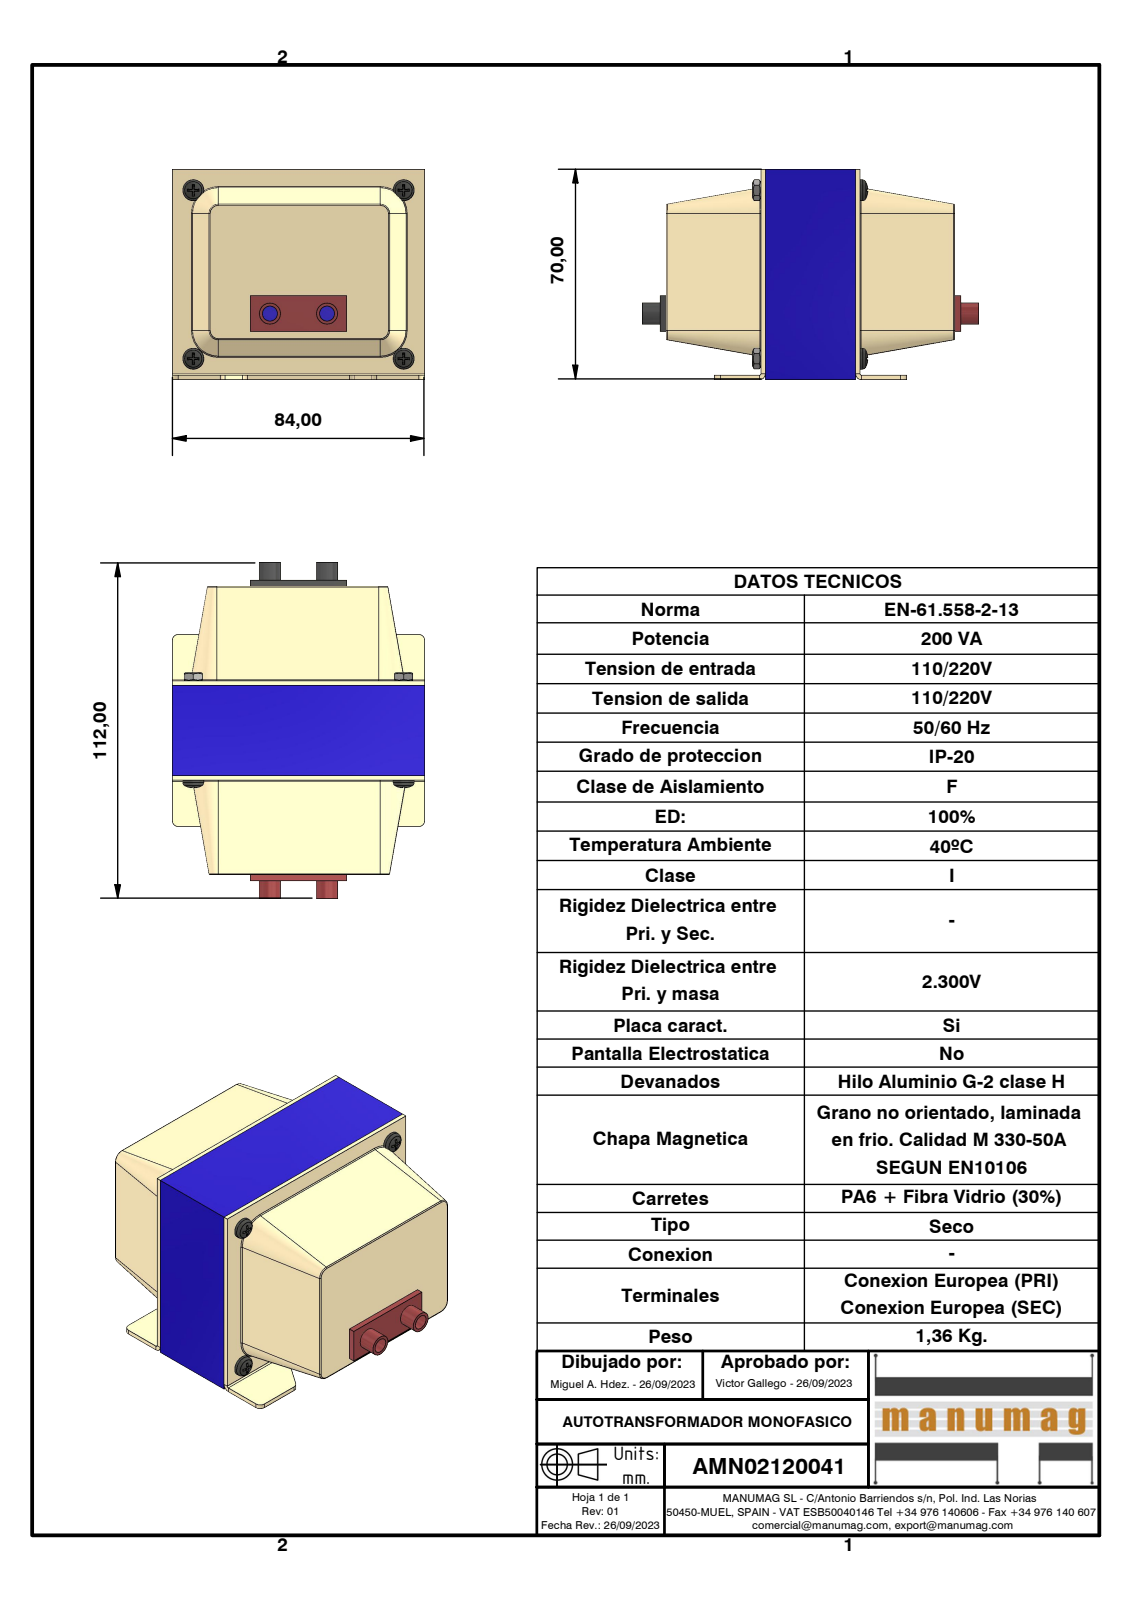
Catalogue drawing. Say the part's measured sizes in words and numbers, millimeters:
The part is named "AMN02120041; EI84 x 70 - 30 (RC28) Azul; TAPA RC28 RECEPTACULO; Receptaculo Rojo (+3 more)". Its 3-D file was written by "Autodesk Inventor 2023 (AUTOMOTIVE_DESIGN)". It is 13 solids with 350 faces: 162 planar, 64 cylindrical and 124 other. Overall it measures 112 by 84 by 70 millimeters. Its volume is 161 805 cubic millimeters and its surface area 82 181 square millimeters. Round holes: 8 of diameter 3, 4 of diameter 2.85, 4 of diameter 4.5, 2 of diameter 5. Round bosses or shafts: 4 of diameter 3.5, 4 of diameter 3.18, 2 of diameter 7. Partial cylindrical surfaces (rounded edges, fillets, slot ends): 16 of radius 0.38, 14 of radius 2, 2 of radius 0.5. The main face-to-face distances are 31.5, 30, 1.5, 63, 33, 60.77, 14, 56, 70, 94.5. The hole center spacings are 70, 89.64, 46.96, 56, 29.58, 29.59, 48.27, 48.28.
